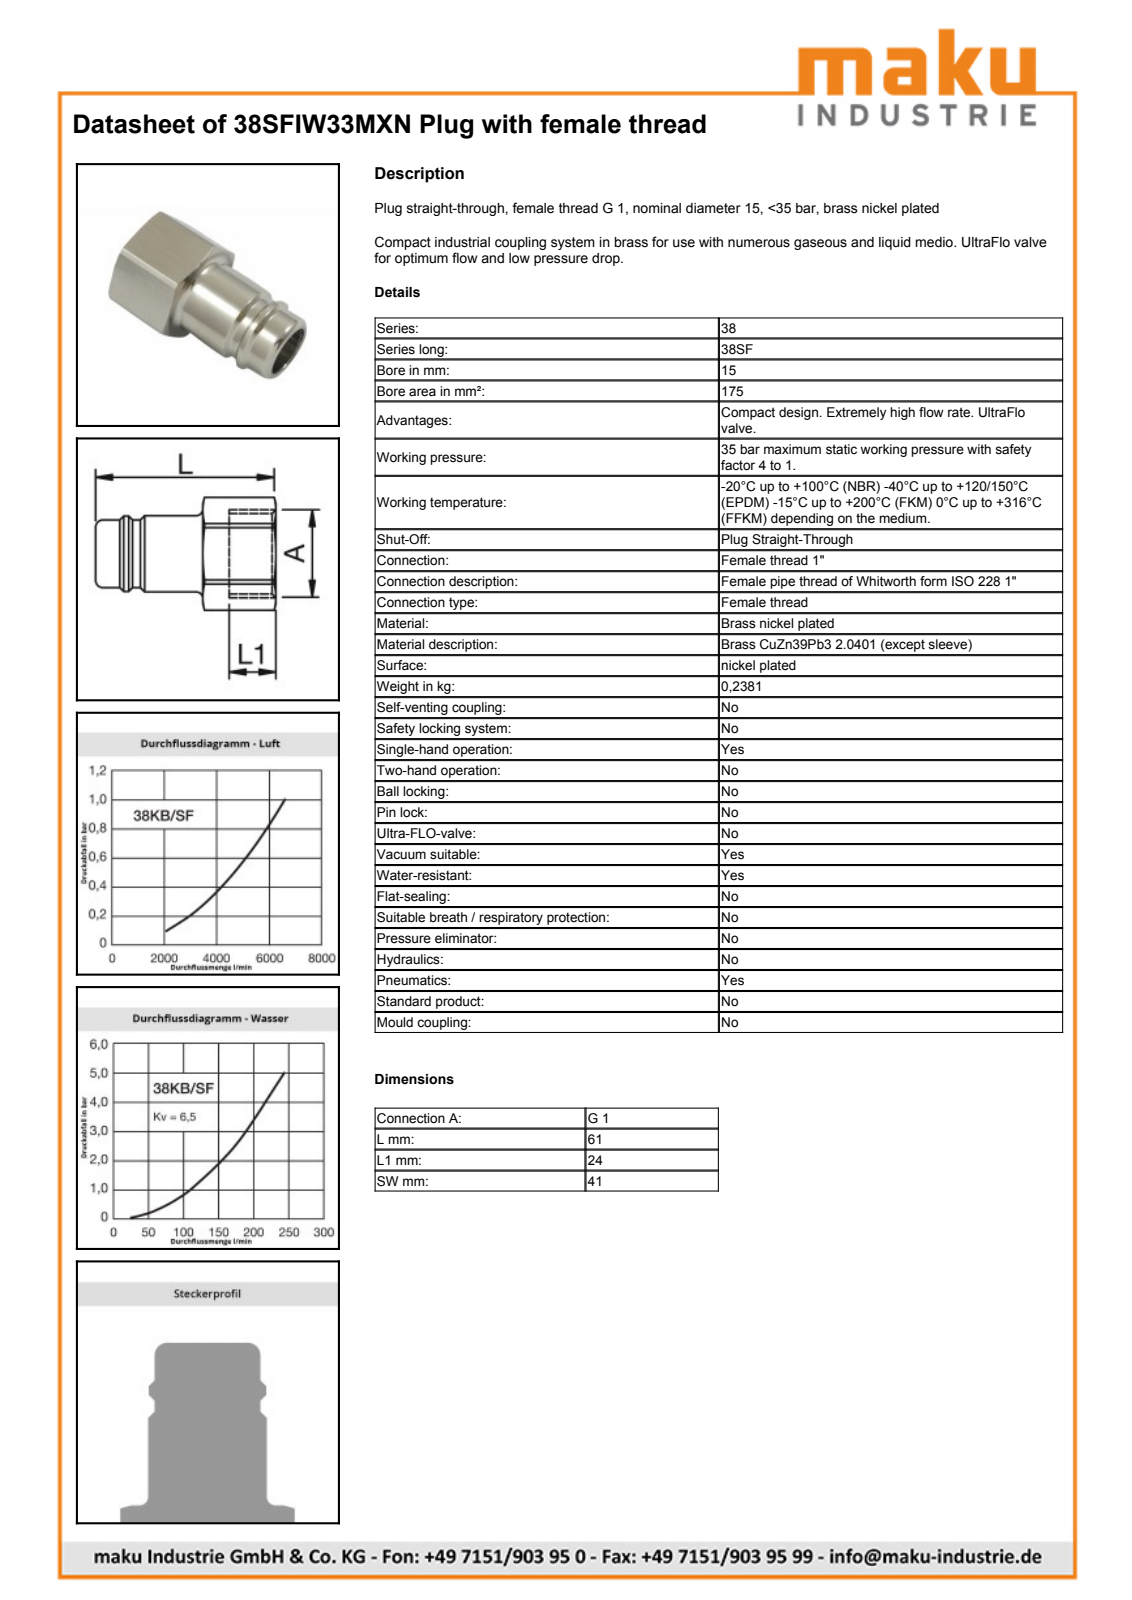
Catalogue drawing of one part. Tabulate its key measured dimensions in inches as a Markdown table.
| quantity | value |
| --- | --- |
| part name | D107540 |
| STEP written by | Autodesk Inventor 2013 (AUTOMOTIVE_DESIGN) |
| units | inches |
| bodies | 1 solid, 40 faces (10 planar, 12 cylindrical, 18 other) |
| overall size | 2.402 × 1.809 × 1.614 |
| volume | 1.618 in³ |
| surface area | 19.81 in² |
| round holes (diameter × count) | 0.591 × 1, 1.309 × 1 |
| round bosses / shafts (diameter × count) | 0.9 × 1, 0.89 × 1, 0.799 × 1 |
| partial cylindrical surfaces (radius × count) | 0.905 × 1 |
| main face-to-face distances | 1.614, 0.193, 1.138, 0.945, 1.264, 1.457, 2.402 |
